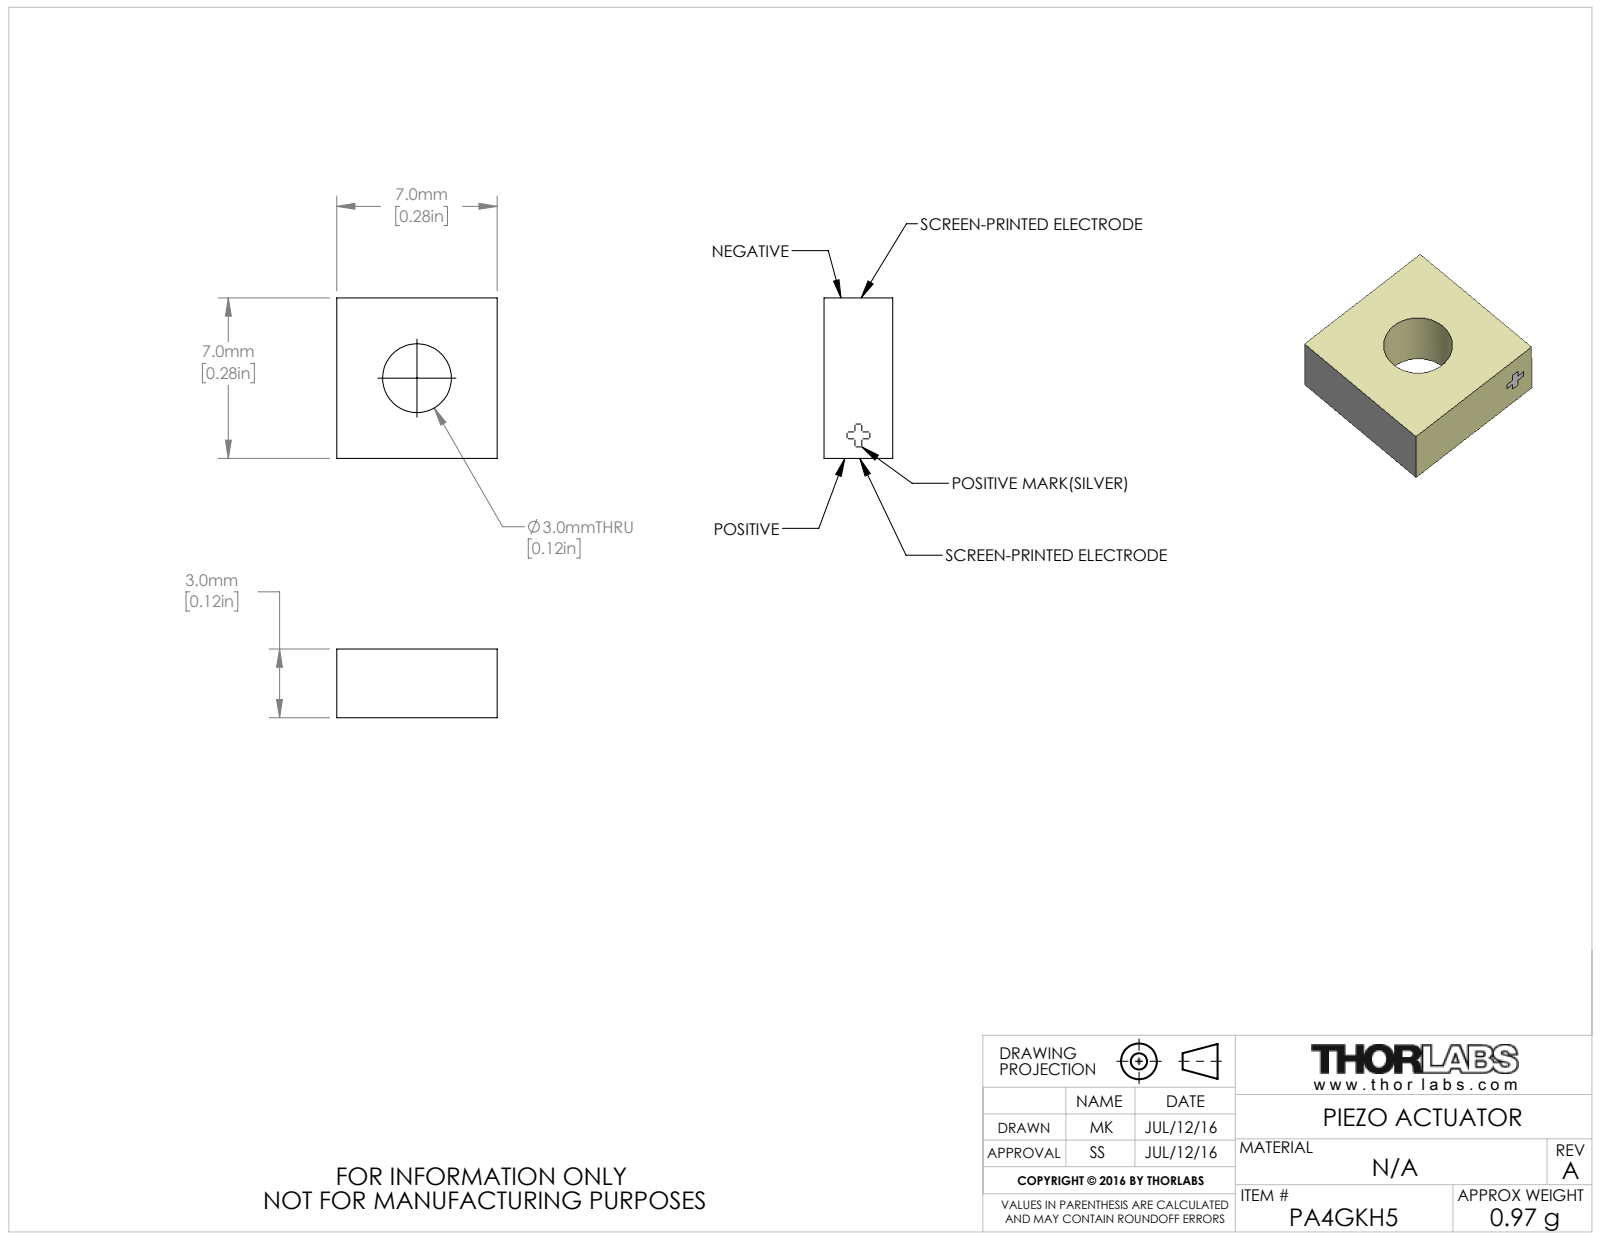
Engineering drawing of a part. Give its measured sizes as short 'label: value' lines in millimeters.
name: CTN009266
written by: SolidWorks 2016 (AUTOMOTIVE_DESIGN)
unit: mm
bodies: 1 solid, 9 faces (7 planar, 2 cylindrical, 0 other)
size: 7 × 7 × 3
volume: 126 mm³; area: 196 mm²
holes: 1× ⌀3
face distances: 7, 3
